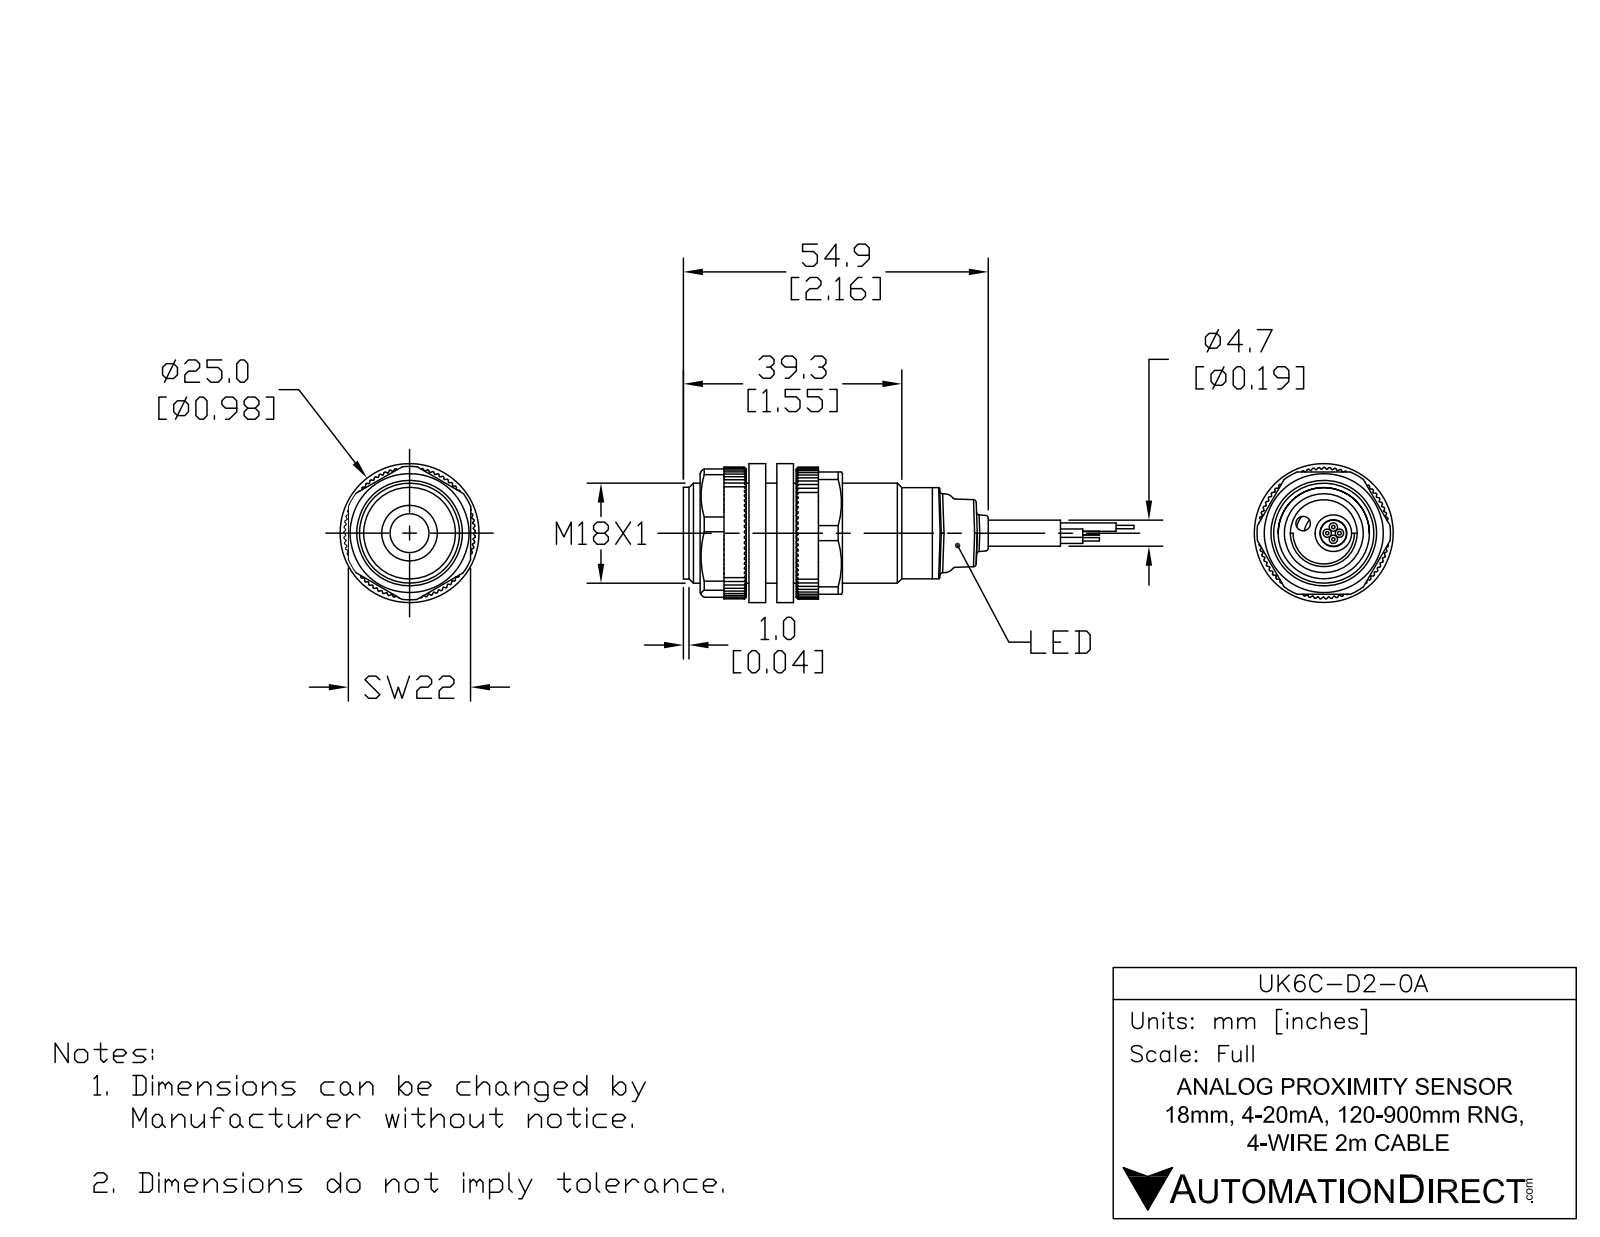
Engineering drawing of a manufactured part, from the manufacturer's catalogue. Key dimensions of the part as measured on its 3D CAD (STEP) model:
Part name (STEP PRODUCT): UK6C-D2-0A
STEP written by: SolidWorks 2017 (AUTOMOTIVE_DESIGN)
Units: inches
Bodies: 4 solids, 62 faces (14 planar, 19 cylindrical, 29 other)
Overall size (bounding box): 3.537 × 0.709 × 0.709
Volume: 0.787 in³ · Surface area: 7.432 in²
Round holes (diameter × count): ⌀0.185 ×1, ⌀0.374 ×1
Round bosses / shafts (diameter × count): ⌀0.709 ×1, ⌀0.646 ×1, ⌀0.622 ×1, ⌀0.559 ×1
Partial cylindrical surfaces — rounded edges, fillets, slot ends (radius × count): R0.008 ×1, R0.02 ×1
Main face-to-face distances: 1.724, 0.039, 1.764, 0.039, 1.763, 1.963, 1.962, 1.923, 0.199, 0.255
Hole centre spacings: 0.068
